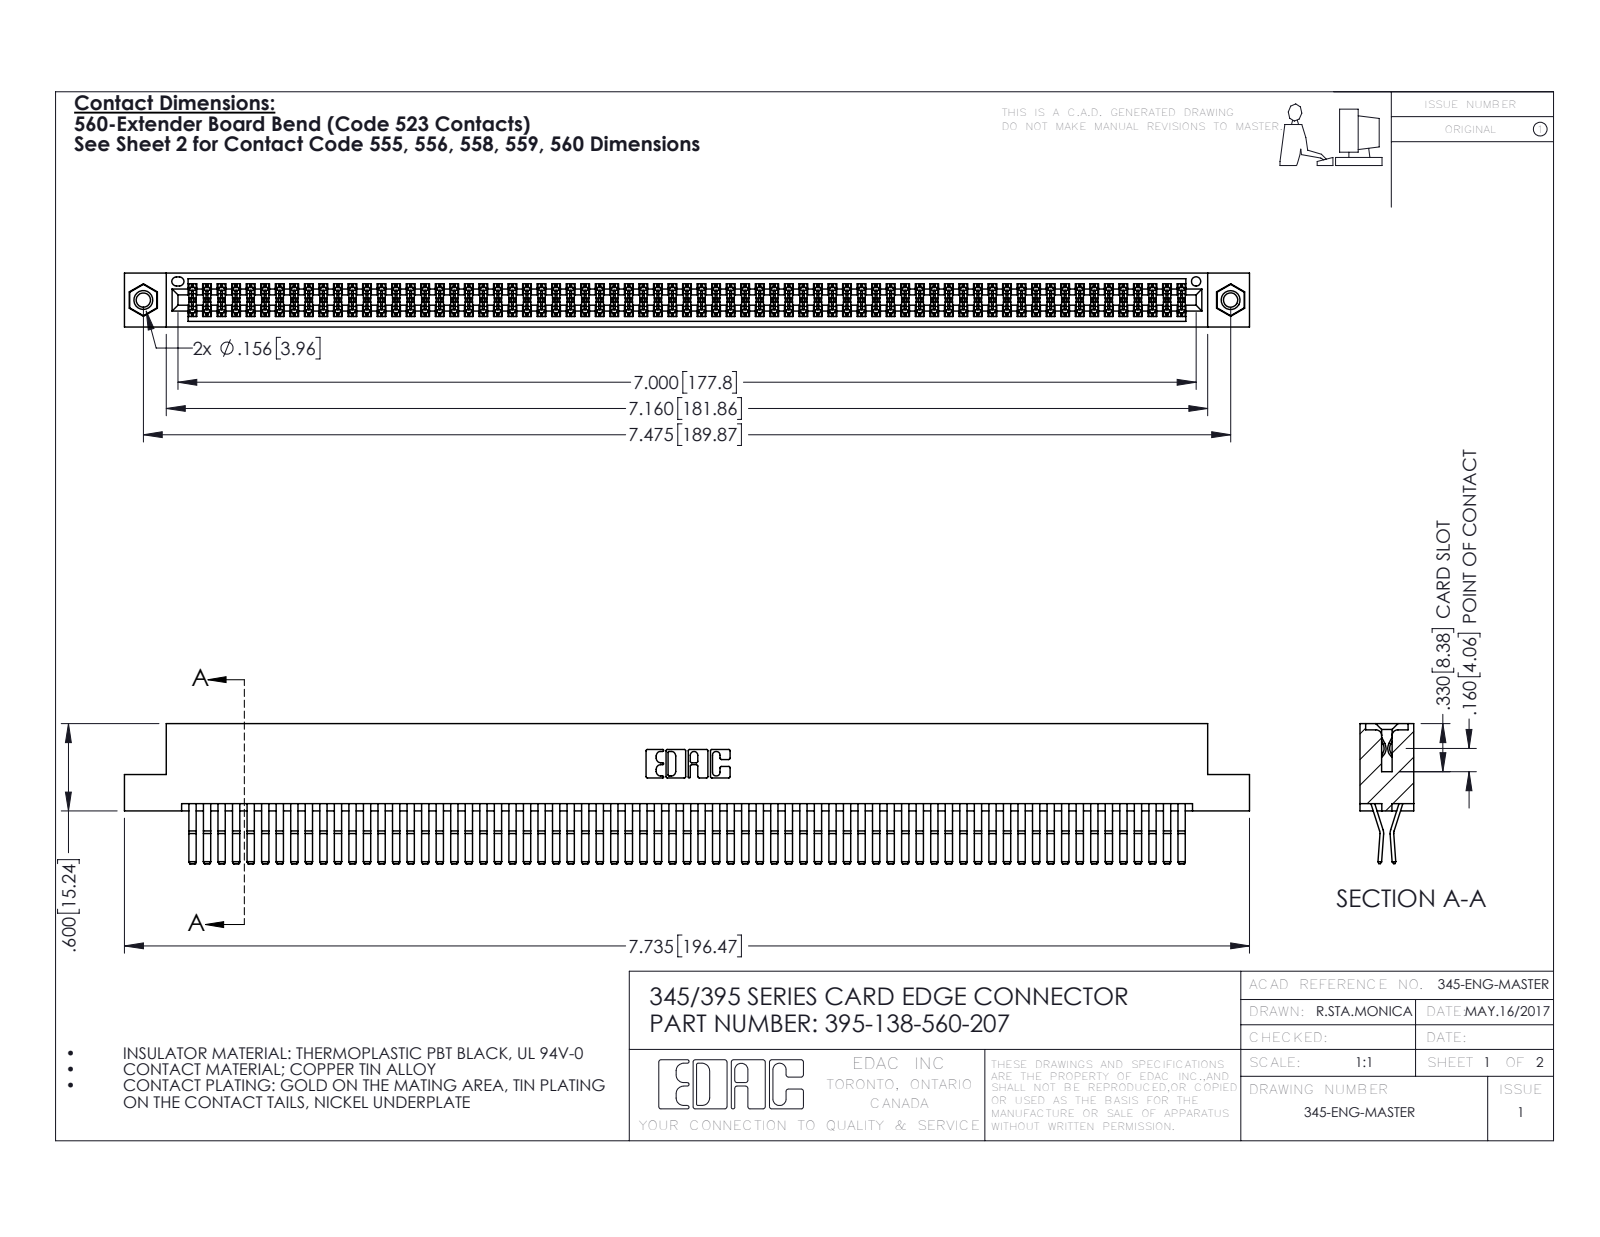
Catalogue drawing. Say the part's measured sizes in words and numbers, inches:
The part is named "395-138-560-207; 345 Part_Flush Mounting Lugs - 0.156 Dia-TI; 345-250-001_345-250-005-103; 345-292-001_560 Tail". Its 3-D file was written by "SolidWorks 2016 (CONFIG_CONTROL_DESIGN)". It is 141 solids with 7362 faces: 4666 planar, 2680 cylindrical and 16 other. Overall it measures 7.735 by 0.962 by 0.37 inches. Its volume is 1.234 cubic inches and its surface area 50.8 square inches. Round holes: 2 of diameter 0.098, 2 of diameter 0.125, 2 of diameter 0.156, 1 of diameter 0.064. Round bosses or shafts: 2 of diameter 0.155. Partial cylindrical surfaces (rounded edges, fillets, slot ends): 207 of radius 0.006, 22 of radius 0.01, 6 of radius 0.007, 6 of radius 0.031, 3 of radius 0.026, 2 of radius 0.01, 2 of radius 0.014, 2 of radius 0.019. The main face-to-face distances are 0.025, 0.072, 0.298, 0.37, 0.2, 0.098, 0.272, 0.225, 0.175, 0.149. The hole center spacings are 0.27, 7.239, 7.475.
